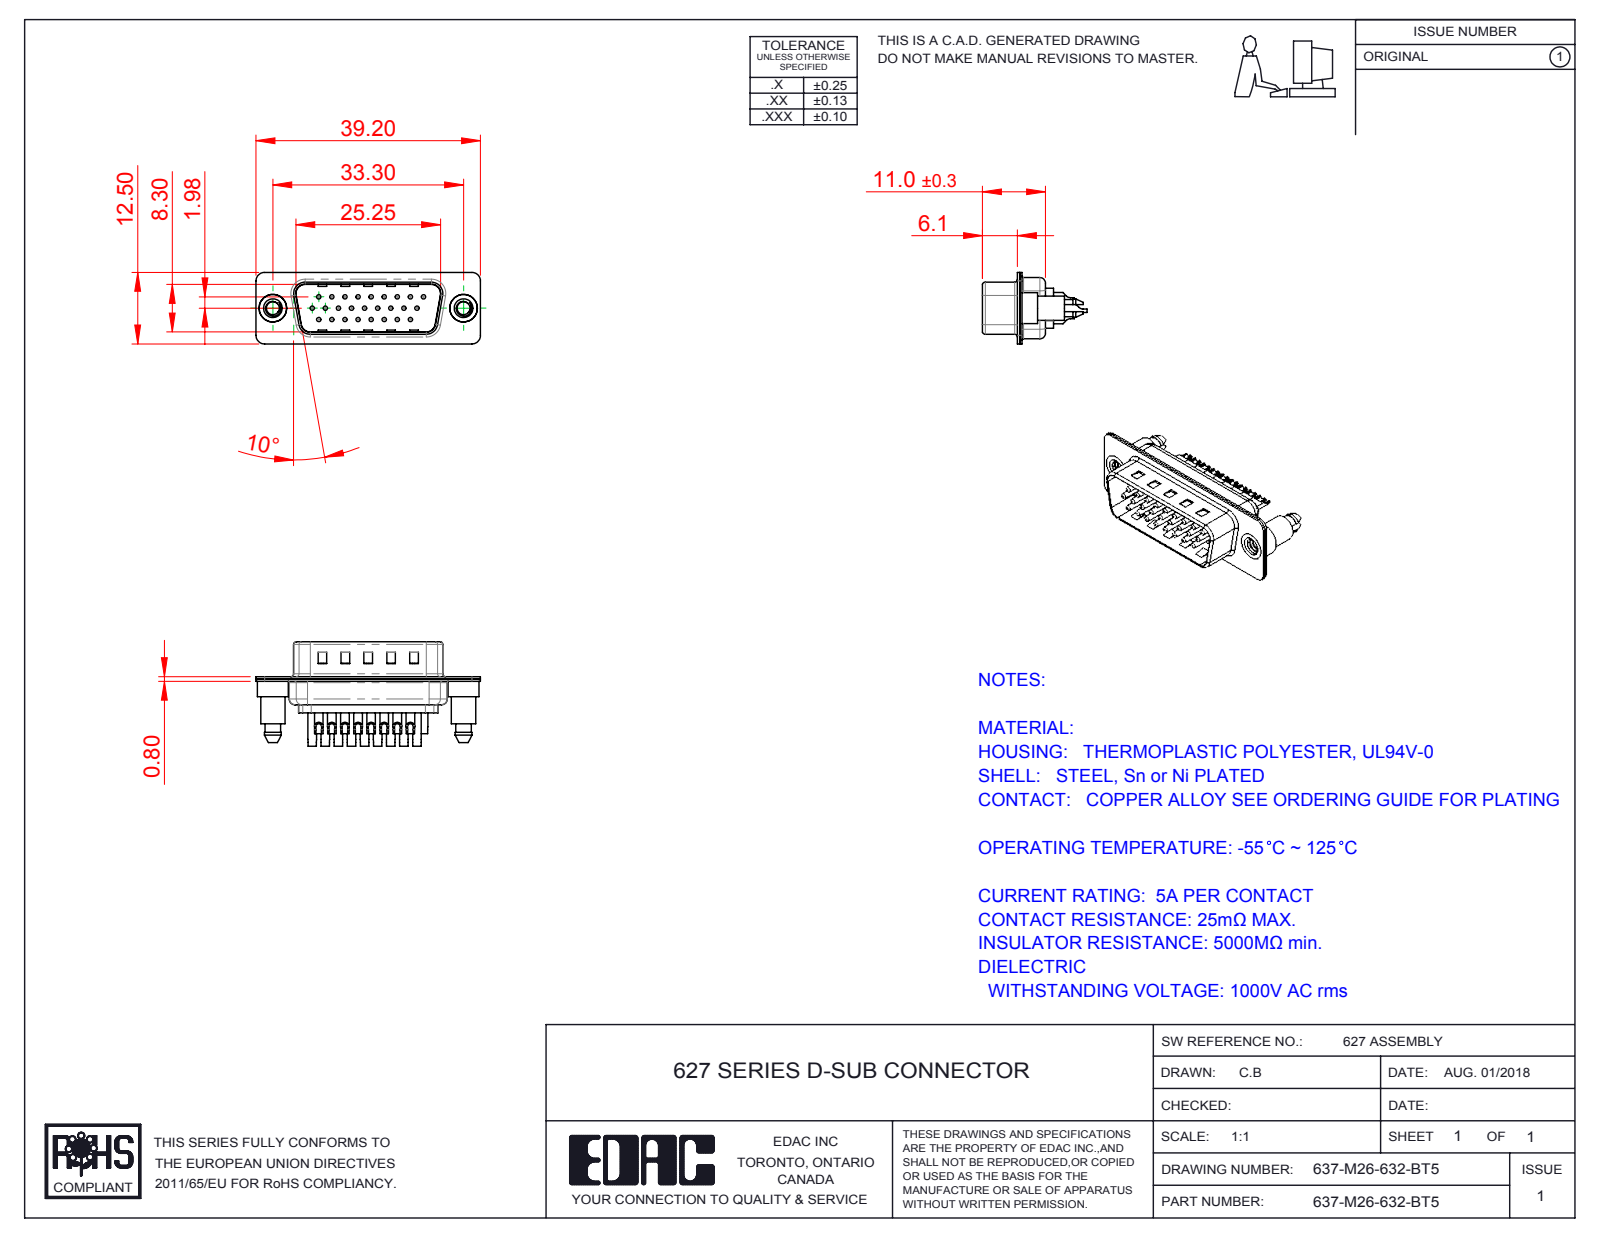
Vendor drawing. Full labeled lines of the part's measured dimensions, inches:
Part name (STEP PRODUCT): 637M Contact Row 3_32; 637-M26-632-BT5; 637M 4-40 Threaded Boardlock; 637M Shell Front_26 Contacts (+4 more)
STEP written by: SolidWorks 2016 (CONFIG_CONTROL_DESIGN)
Units: inches
Bodies: 31 solids, 1352 faces (389 planar, 581 cylindrical, 382 other)
Overall size (bounding box): 1.543 × 0.719 × 0.492
Volume: 0.13 in³ · Surface area: 9.929 in²
Round holes (diameter × count): ⌀0.03 ×26, ⌀0.039 ×26, ⌀0.063 ×26, ⌀0.079 ×26, ⌀0.089 ×2, ⌀0.157 ×2, ⌀0.189 ×2
Round bosses / shafts (diameter × count): ⌀0.059 ×26, ⌀0.213 ×2, ⌀0.193 ×2, ⌀0.167 ×2
Partial cylindrical surfaces — rounded edges, fillets, slot ends (radius × count): R0.059 ×18, R0.079 ×12, R0.063 ×10, R0.02 ×8, R0.039 ×7, R0.01 ×4, R0.024 ×4, R0.026 ×4
Main face-to-face distances: 0.016, 0.031, 0.374, 0.358, 0.343, 0.39, 0.03, 0.014, 0.047, 0.075
Hole centre spacings: 0.156, 0.09, 0.18, 0.238, 0.09, 0.324, 0.27, 0.413
